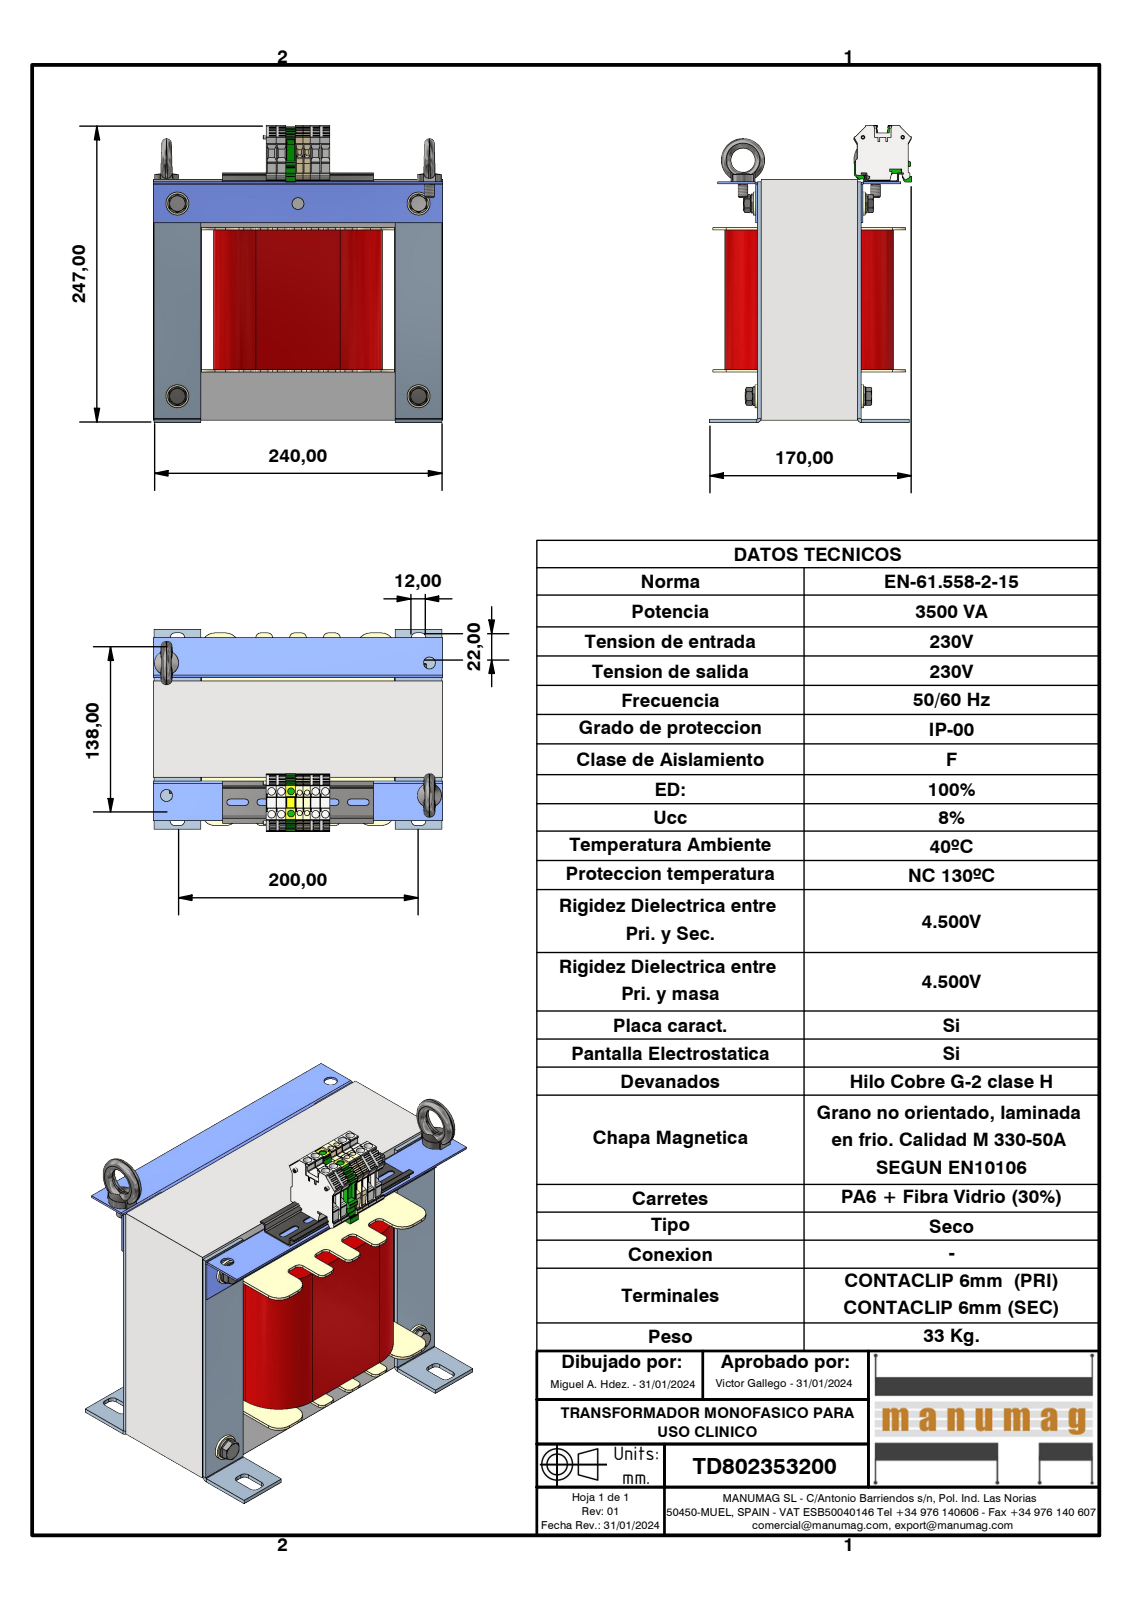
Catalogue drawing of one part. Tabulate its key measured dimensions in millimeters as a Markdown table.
| quantity | value |
| --- | --- |
| part name | TD802353200; EI240 240 x 200 - 80 (Rc80); SEMI 40 X 60 RC80 EI240 - 40; Escuadra RC80 (+8 more) |
| STEP written by | Autodesk Inventor 2023 (AUTOMOTIVE_DESIGN) |
| units | millimeters |
| bodies | 42 solids, 2415 faces (1680 planar, 567 cylindrical, 168 other) |
| overall size | 247.05 × 240 × 168.1 |
| volume | 4 799 000 mm³ |
| surface area | 583 000 mm² |
| round holes (diameter × count) | 6.3 × 8, 10 × 7, 2.4 × 4, 2.5 × 4, 2.75 × 4, 4.3 × 4, 6.65 × 4, 8 × 4, 8.4 × 4, 11 × 4, 12 × 4, 2.95 × 2 |
| round bosses / shafts (diameter × count) | 19 × 4, 16 × 4, 11.4 × 4, 9.6 × 4, 7.32 × 4, 36 × 2, 8 × 2, 7 × 2 |
| partial cylindrical surfaces (radius × count) | 4 × 48, 0.3 × 30, 1 × 22, 0.25 × 17, 0.5 × 13, 2.6 × 10, 2 × 9, 0.4 × 8 |
| main face-to-face distances | 80, 160, 40, 3, 200, 83, 120, 2, 1.5, 30 |
| hole center spacings | 8.1, 15.23, 19, 20.65, 21.32, 23.56, 27.89, 36.5 |
